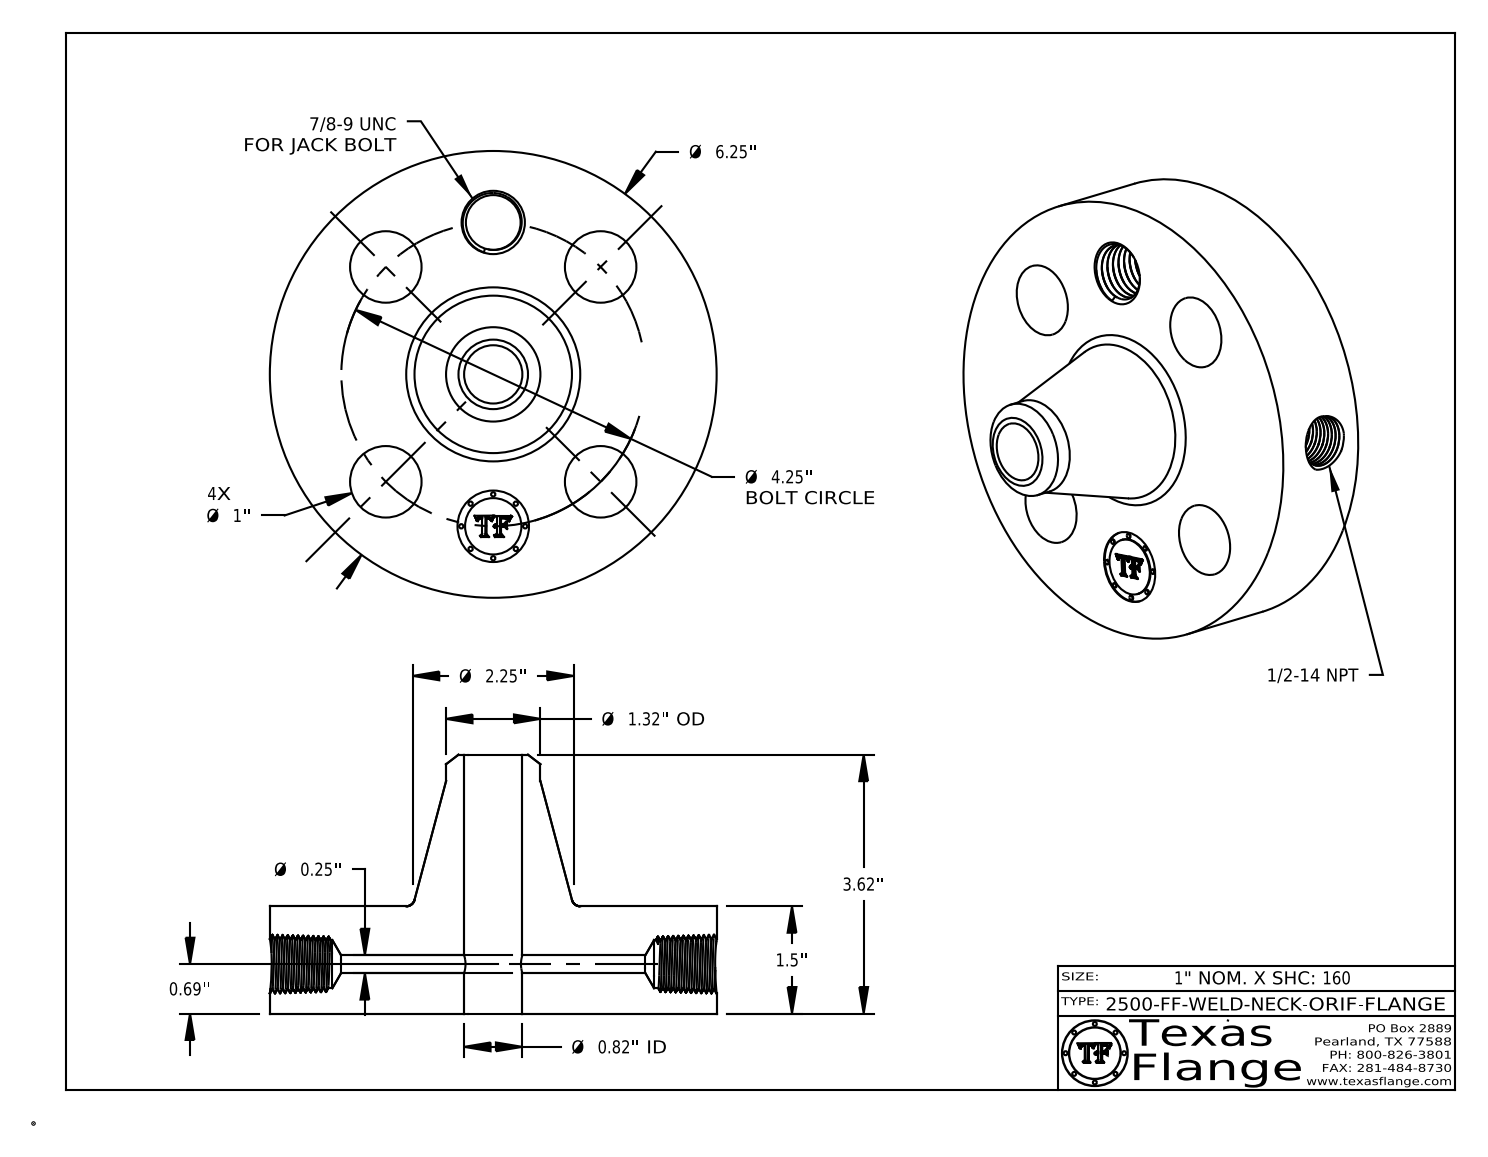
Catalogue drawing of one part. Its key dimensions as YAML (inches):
part_name: "2500-FF-WELD-NECK"
step_written_by: "CATIA V5 STEP AP214 (AUTOMOTIVE_DESIGN)"
units: inches
bodies: {solids: 1, faces: 748, planar: 368, cylindrical: 80, other: 300}
overall_size: [6.25, 6.25, 3.62]
volume: 42.62
surface_area: 134.1
round_holes:
  - {diameter: 1, count: 5}
  - {diameter: 0.25, count: 1}
  - {diameter: 0.672, count: 1}
  - {diameter: 0.766, count: 1}
  - {diameter: 0.815, count: 1}
round_bosses_or_shafts:
  - {diameter: 0.061, count: 8}
  - {diameter: 6.25, count: 1}
  - {diameter: 1.32, count: 1}
  - {diameter: 0.788, count: 1}
face_to_face_distances: [1.5, 0.015, 1.485, 3.62, 2.135, 2.12, 0.298, 0.292, 0.054, 0.248]
hole_center_spacings: [2.125, 1.626, 3.006, 3.927, 4.25]
